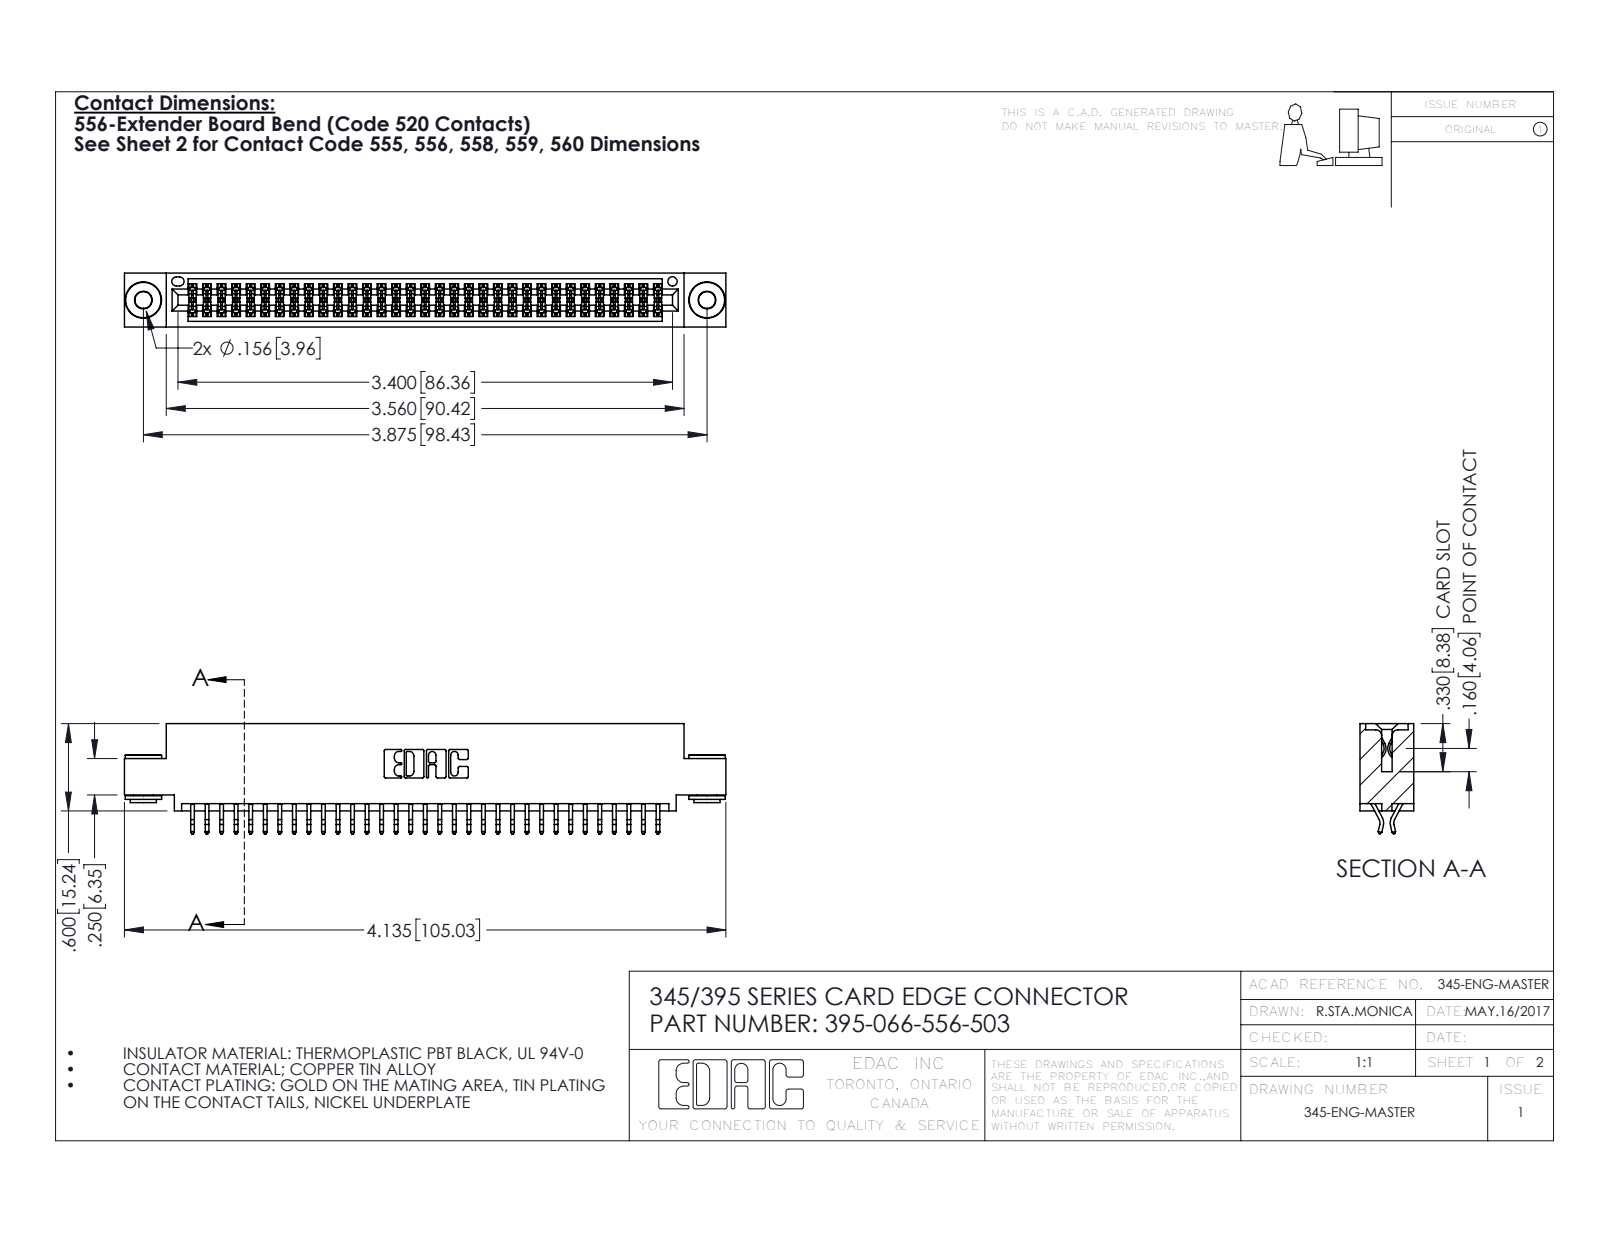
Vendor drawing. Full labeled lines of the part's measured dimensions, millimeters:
Part name (STEP PRODUCT): 345 Part_0.110 Offset - 0.156 Dia-TH; 345-250-002_345-250-002-102; 395-066-556-503; 345-292-001_556 Tail
STEP written by: SolidWorks 2016 (CONFIG_CONTROL_DESIGN)
Units: millimetres
Bodies: 69 solids, 3864 faces (2536 planar, 1320 cylindrical, 8 other)
Overall size (bounding box): 105 × 19.2 × 9.4
Volume: 10 100 mm³ · Surface area: 14 940 mm²
Round holes (diameter × count): ⌀2.9 ×2, ⌀4 ×2, ⌀1.6 ×1
Round bosses / shafts (diameter × count): ⌀6.4 ×2, ⌀4.6 ×2, ⌀3.5 ×2
Partial cylindrical surfaces — rounded edges, fillets, slot ends (radius × count): R0.2 ×99, R0.3 ×22, R0.2 ×6, R0.8 ×6, R0.7 ×3, R0.3 ×2, R0.4 ×2, R0.5 ×2
Main face-to-face distances: 1.8, 7.6, 9.4, 5.1, 0.6, 2.5, 6.9, 5.7, 4.4, 3.8
Hole centre spacings: 6.9, 92.5, 98.4
